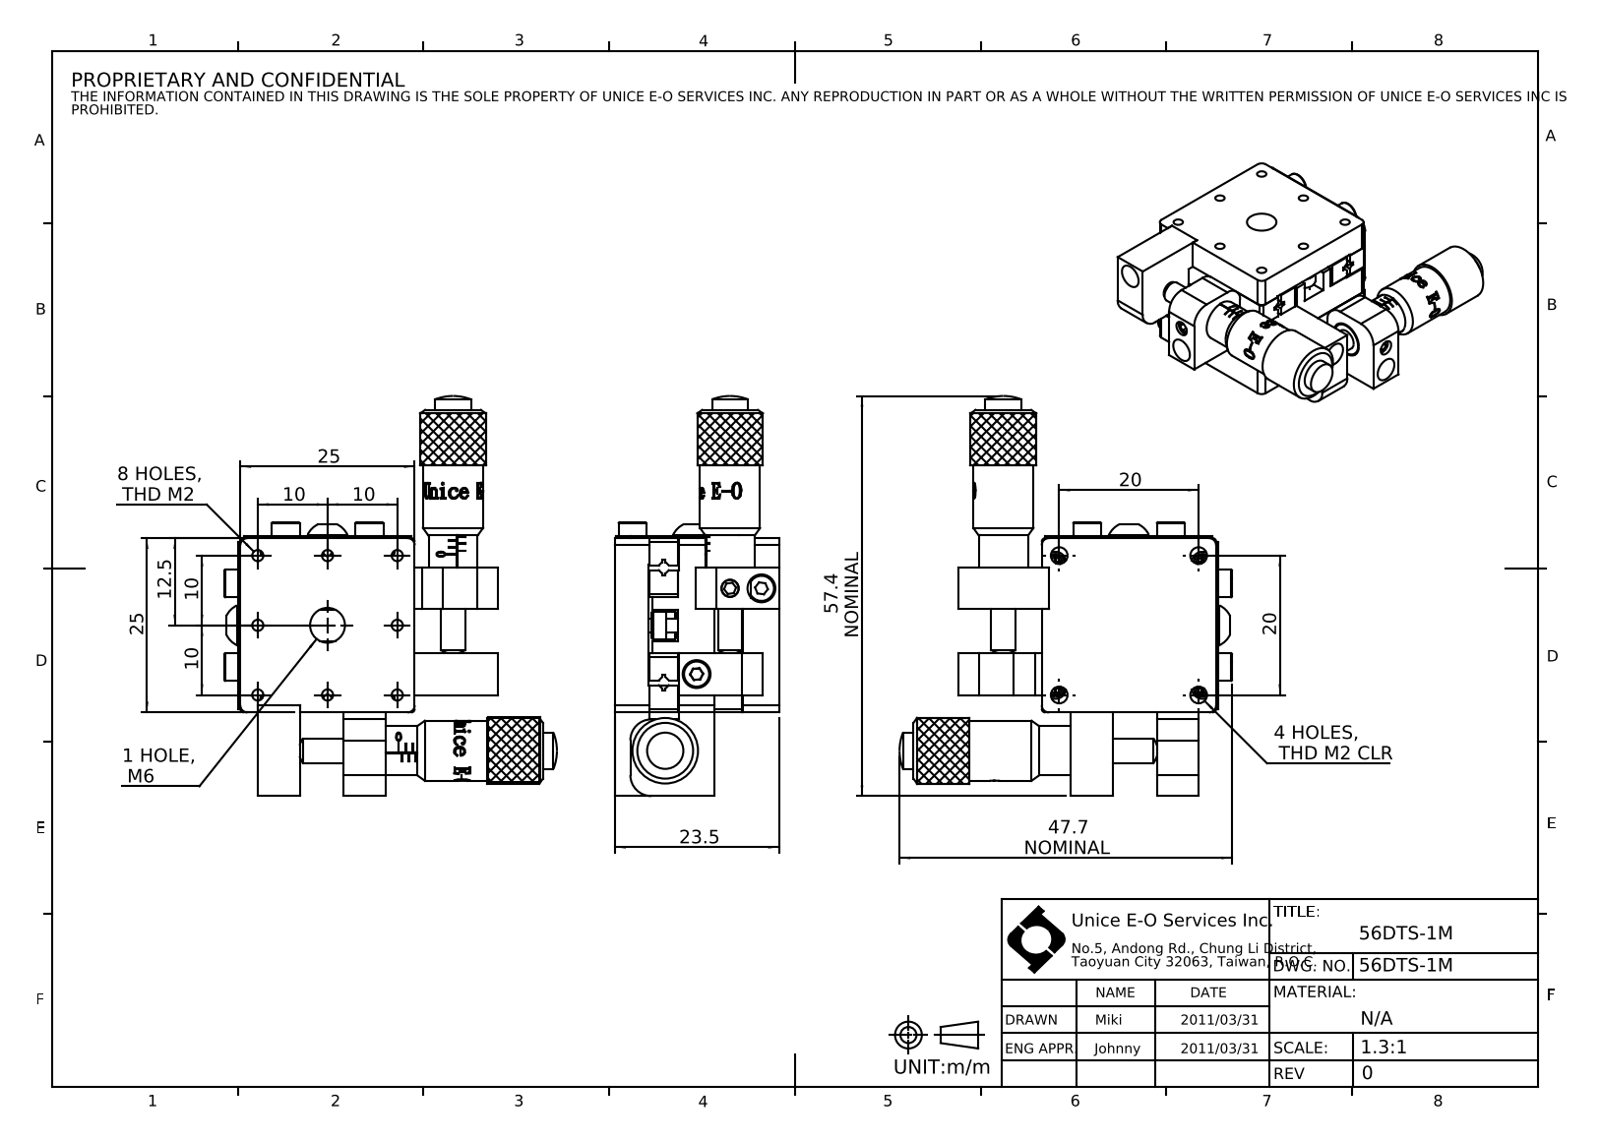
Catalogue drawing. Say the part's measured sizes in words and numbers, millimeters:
The part is named "56DTS-1M". Its 3-D file was written by "SolidWorks 2016 (CONFIG_CONTROL_DESIGN)". It is 65 solids with 2441 faces: 1181 planar, 680 cylindrical and 580 other. Overall it measures 57.4 by 47.7 by 23.5 millimeters. Its volume is 18 369 cubic millimeters and its surface area 21 587 square millimeters. Round holes: 24 of diameter 1.25, 24 of diameter 1.8, 24 of diameter 3.1, 16 of diameter 1.6, 8 of diameter 2.4, 4 of diameter 1.2, 4 of diameter 2.2, 4 of diameter 2.5, 4 of diameter 4.4, 3 of diameter 4, 2 of diameter 3, 2 of diameter 3.5. Round bosses or shafts: 24 of diameter 2.5, 24 of diameter 1.4, 12 of diameter 2, 9 of diameter 4, 4 of diameter 5.7, 4 of diameter 3, 2 of diameter 9.4, 2 of diameter 8.6. Partial cylindrical surfaces (rounded edges, fillets, slot ends): 96 of radius 0.1, 12 of radius 0.5, 8 of radius 2, 8 of radius 3, 4 of radius 1, 4 of radius 1.8, 2 of radius 4.28. The main face-to-face distances are 9.2, 4.2, 9, 16.5, 5, 4, 8.5, 25, 14.5, 4.8. The hole center spacings are 9, 10.11, 18.79, 14.92, 4.6, 16.5, 18, 4.17.
